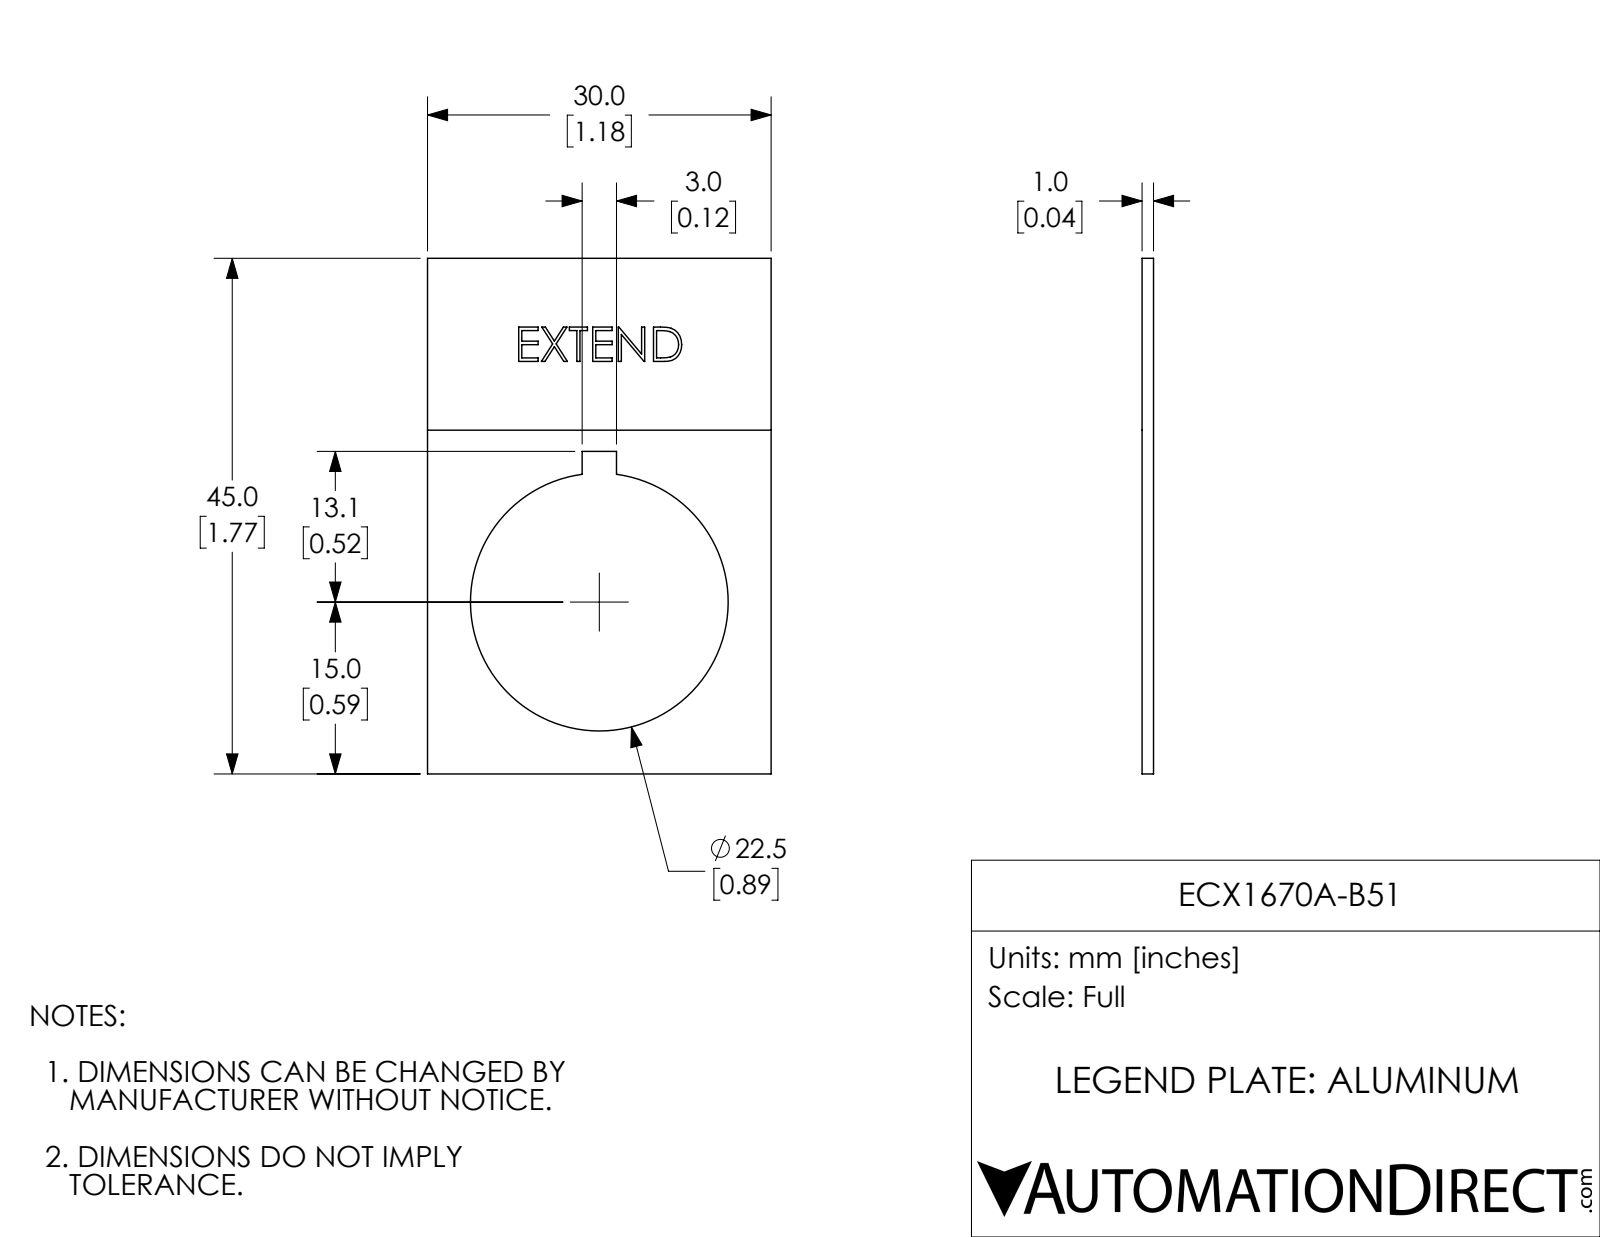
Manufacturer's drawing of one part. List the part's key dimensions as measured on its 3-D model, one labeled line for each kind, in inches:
Part name (STEP PRODUCT): ECX1670A-B51
STEP written by: SolidWorks 2017 (AUTOMOTIVE_DESIGN)
Units: inches
Bodies: 1 solid, 87 faces (77 planar, 3 cylindrical, 7 other)
Overall size (bounding box): 1.772 × 1.181 × 0.039
Volume: 0.058 in³ · Surface area: 3.286 in²
Round holes (diameter × count): ⌀0.886 ×1
Main face-to-face distances: 0.039, 1.181, 1.772, 0.038, 0.531, 0.65, 1.108, 0.663, 0.118, 0.012
